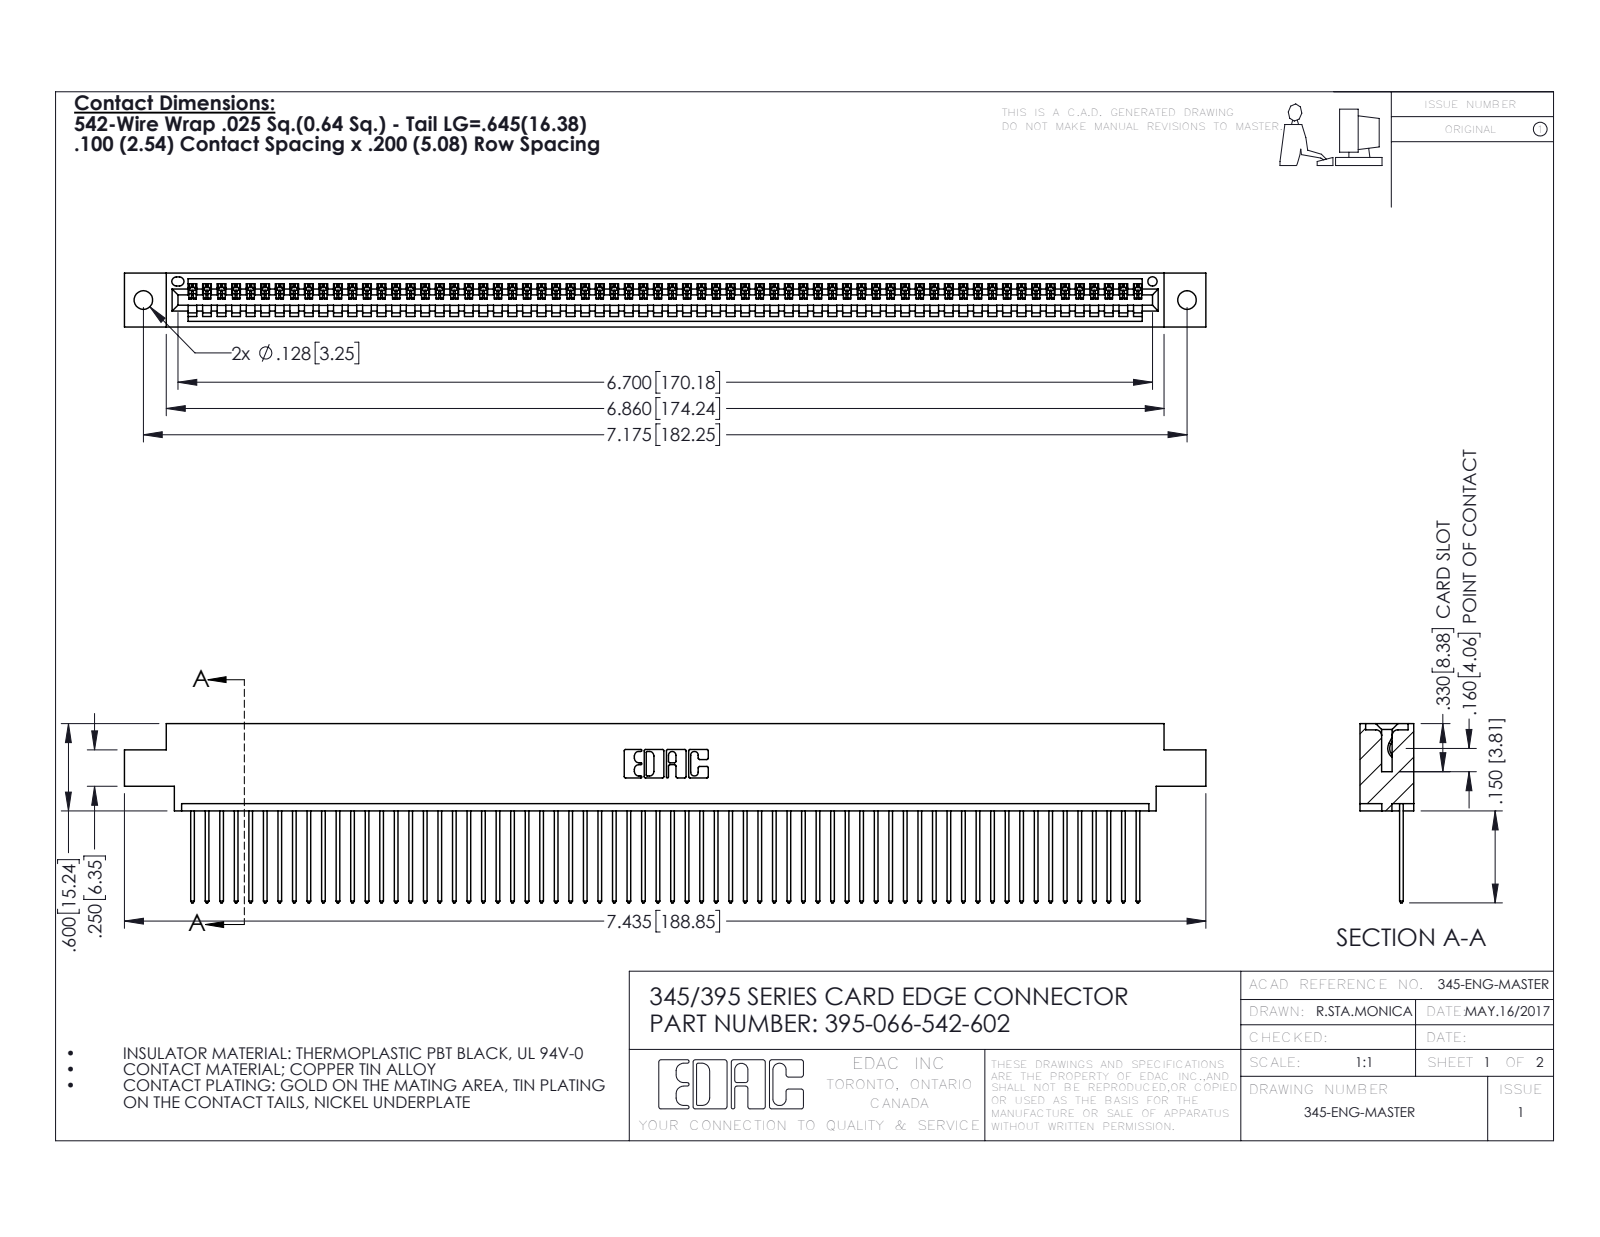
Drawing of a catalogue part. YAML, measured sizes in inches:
part_name: "345 Part_0.170 Offset - 0.128 Dia; 345-292-001_345-293-142; 395-066-542-602"
step_written_by: "SolidWorks 2016 (CONFIG_CONTROL_DESIGN)"
units: inches
bodies: {solids: 67, faces: 3958, planar: 2724, cylindrical: 1234, other: 0}
overall_size: [7.435, 1.232, 0.37]
volume: 1.106
surface_area: 39.07
round_holes:
  - {diameter: 0.128, count: 2}
  - {diameter: 0.064, count: 1}
partial_cylinders:
  - {radius: 0.006, count: 132}
  - {radius: 0.01, count: 132}
  - {radius: 0.01, count: 22}
  - {radius: 0.007, count: 6}
  - {radius: 0.031, count: 6}
  - {radius: 0.026, count: 3}
  - {radius: 0.031, count: 2}
  - {radius: 0.04, count: 2}
face_to_face_distances: [0.072, 0.298, 0.37, 0.098, 0.272, 0.025, 0.2, 0.225, 0.175, 0.149]
hole_center_spacings: [0.27, 6.939, 7.175]
